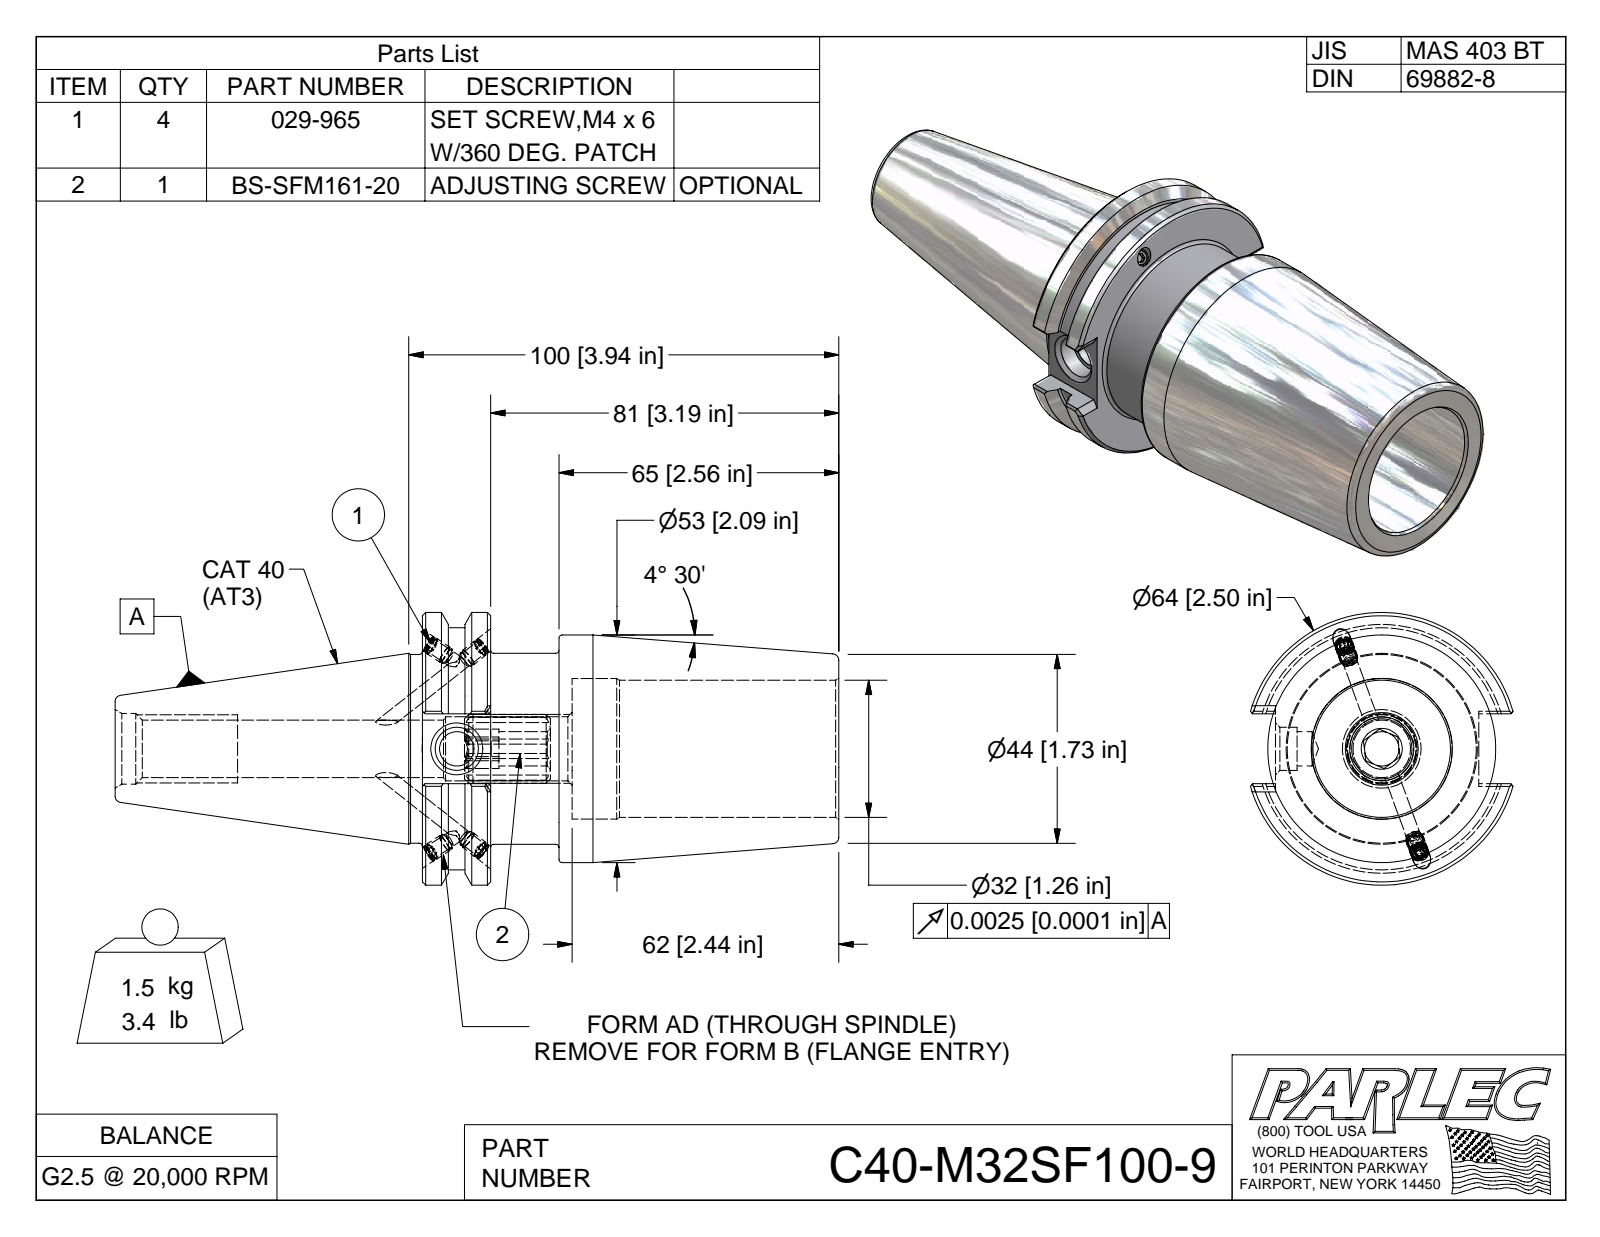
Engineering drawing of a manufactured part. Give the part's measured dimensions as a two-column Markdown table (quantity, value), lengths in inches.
| quantity | value |
| --- | --- |
| part name | C40-M32SF100-9; C40BC-M32SF100-9-1; 029-965; BS-SFM161-20 |
| STEP written by | Autodesk Inventor 2009 (AUTOMOTIVE_DESIGN) |
| units | inches |
| bodies | 6 solids, 176 faces (88 planar, 33 cylindrical, 55 other) |
| overall size | 6.625 × 2.5 × 2.403 |
| volume | 12 in³ |
| surface area | 66.61 in² |
| round holes (diameter × count) | 0.13 × 4, 0.161 × 4, 1.258 × 1, 1.288 × 1 |
| round bosses / shafts (diameter × count) | 0.165 × 4, 0.157 × 4, 2.5 × 1, 2.219 × 1, 2.087 × 1, 1.75 × 1, 1.73 × 1 |
| partial cylindrical surfaces (radius × count) | 0.315 × 1 |
| main face-to-face distances | 0.625, 1.371, 0.746, 3.812, 3.187, 2.441, 1.25, 0.121, 2.562, 0.64 |
